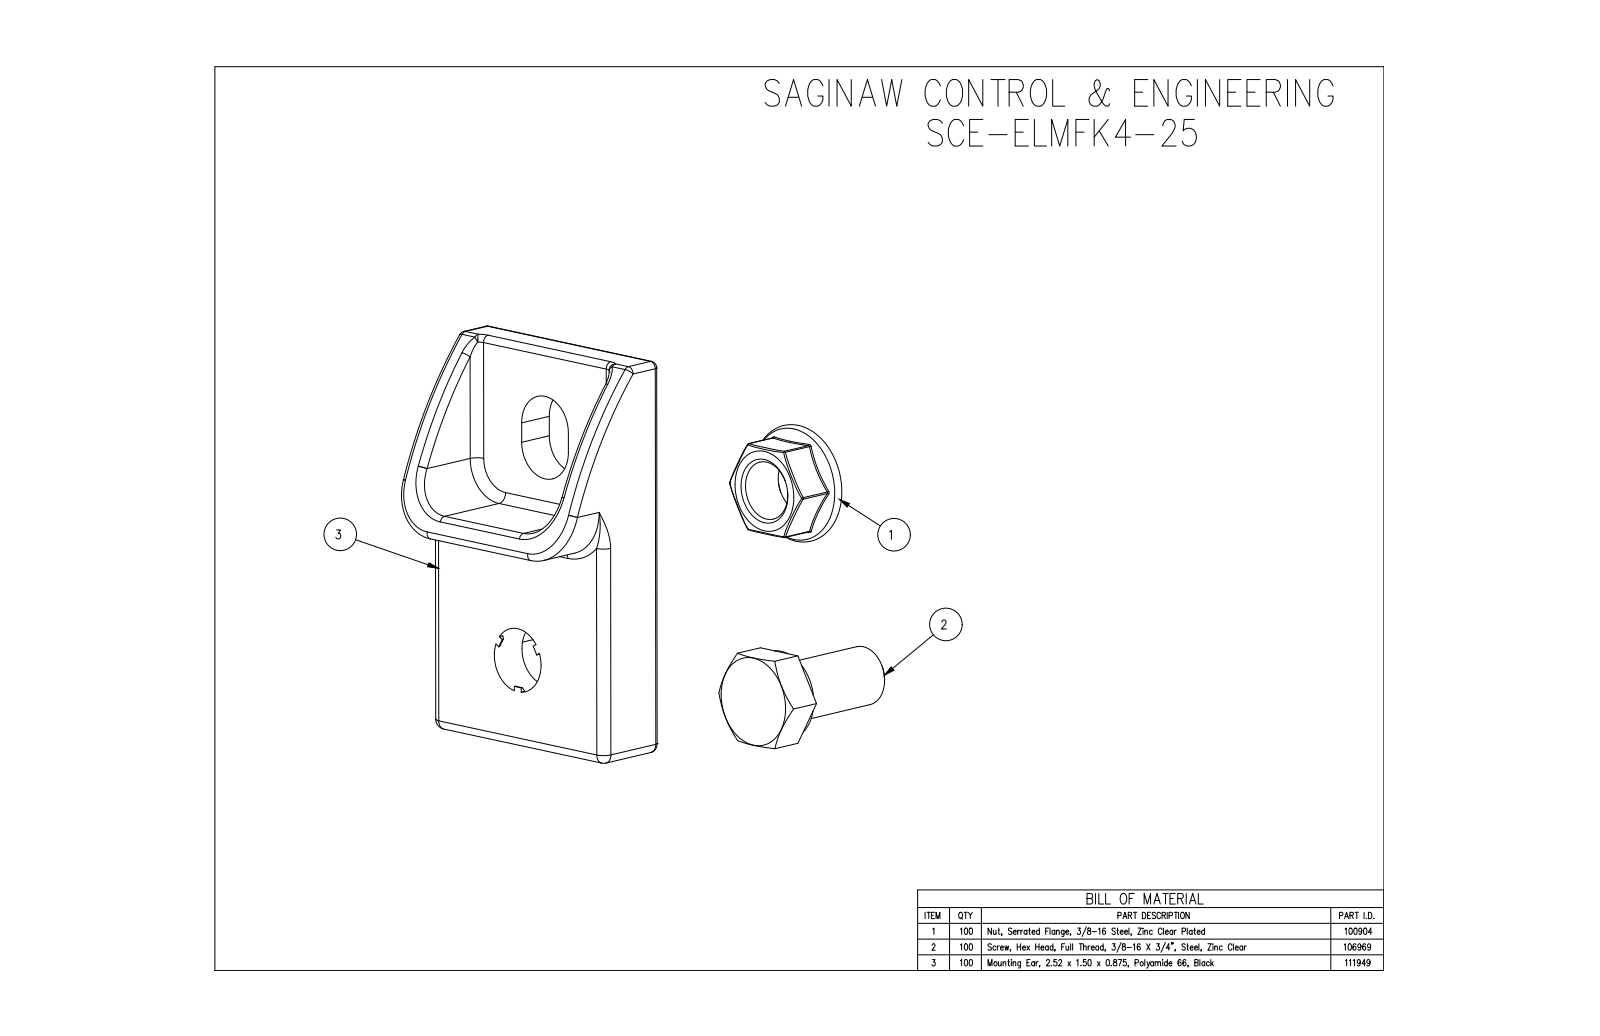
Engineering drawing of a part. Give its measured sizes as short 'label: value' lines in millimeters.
name: SCE-ELMFK4-25
written by: SolidWorks 2019 (AUTOMOTIVE_DESIGN)
unit: mm
bodies: 12 solids, 804 faces (328 planar, 224 cylindrical, 252 other)
size: 213.7 × 152.4 × 25.5
volume: 111 200 mm³; area: 45 600 mm²
holes: 4× ⌀9.3, 4× ⌀10.3
bosses: 4× ⌀14.3, 4× ⌀9.5
rounds: 88× R0.8, 24× R0.3, 18× R1, 8× R1.6, 8× R5.2, 8× R6.4, 6× R1.5, 6× R1.6
face distances: 6.4, 12.7, 114.3, 38.1, 4.7, 152.4, 76.2, 4, 123.4, 1.6
hole spacings: 114.3, 161.6, 114.3, 161.6
